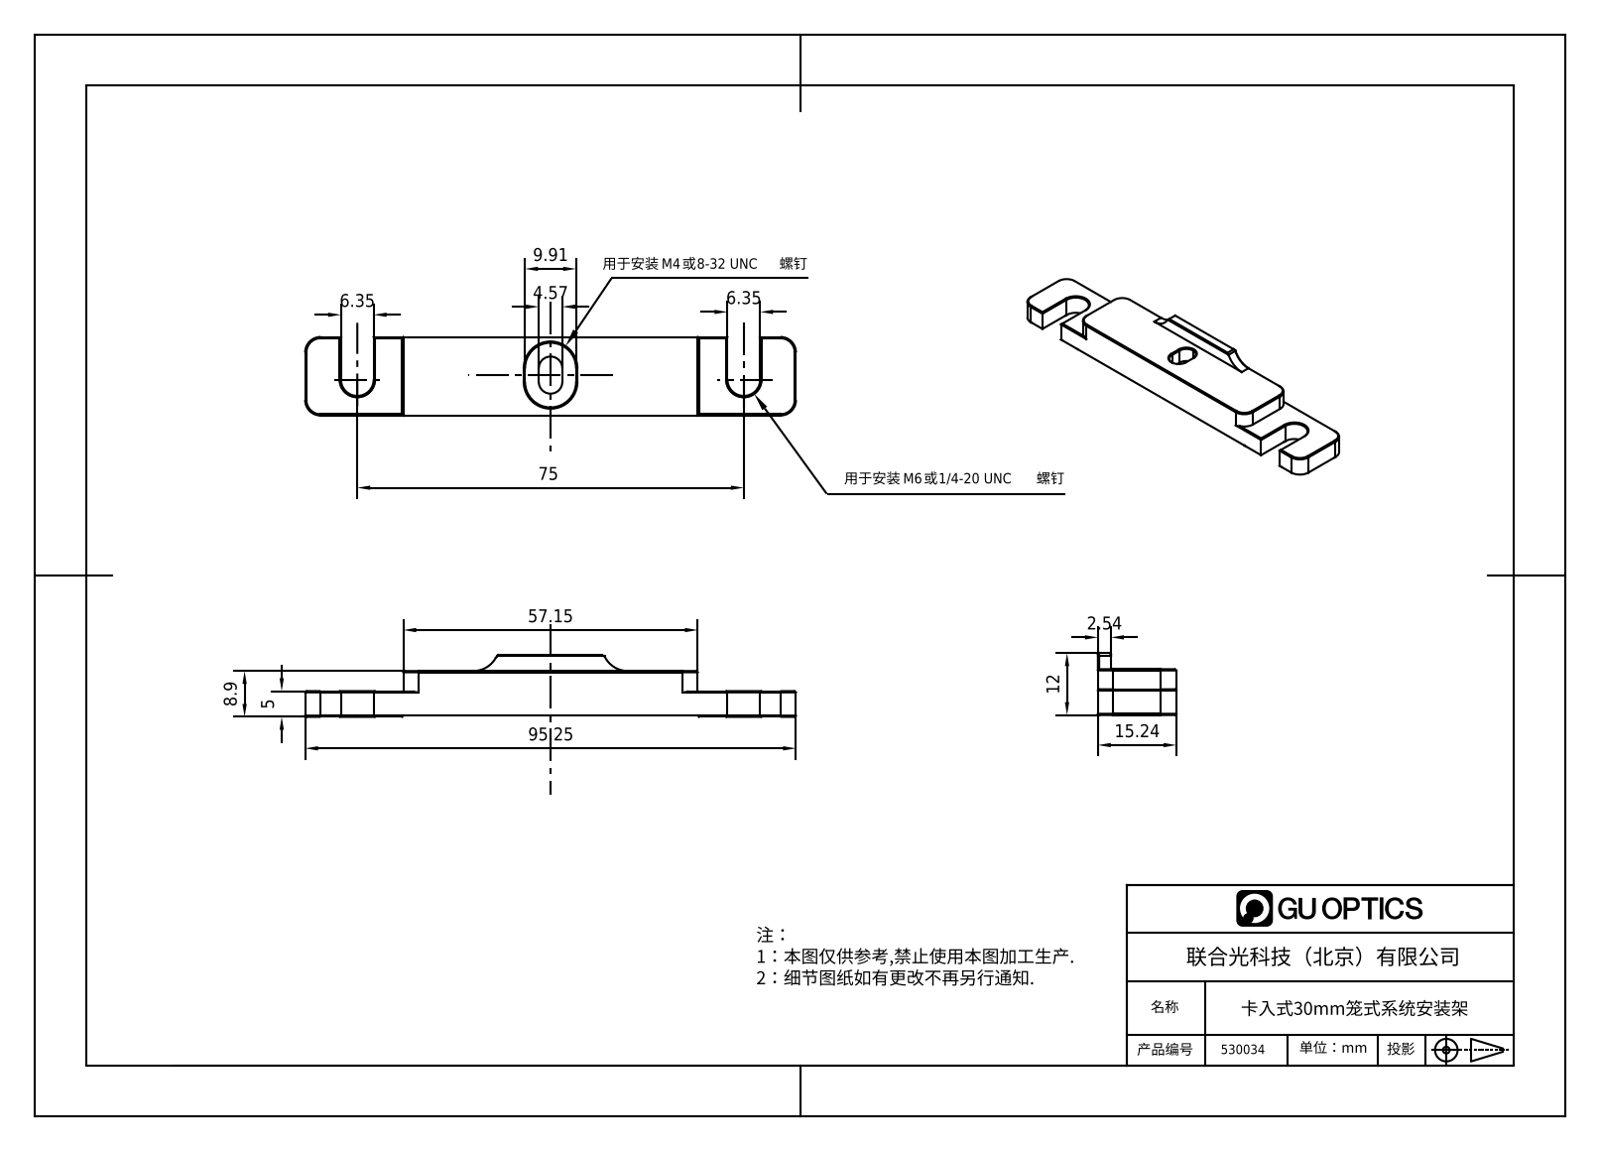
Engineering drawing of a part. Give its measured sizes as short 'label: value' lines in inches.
name: 2.4.4.8_LZA-ZB30_30mm笼式系统笼板安装座
written by: SolidWorks 2018 (AUTOMOTIVE_DESIGN)
unit: in
bodies: 0 solids, 110 faces (66 planar, 18 cylindrical, 26 other)
size: 3.75 × 0.6 × 0.472
rounds: 8× R0.118, 2× R0.09, 2× R0.125, 2× R0.195, 2× R0.197
face distances: 0.341, 0.6, 0.187, 0.154, 0.197, 0.35, 0.523, 0.2, 0.19, 0.15
